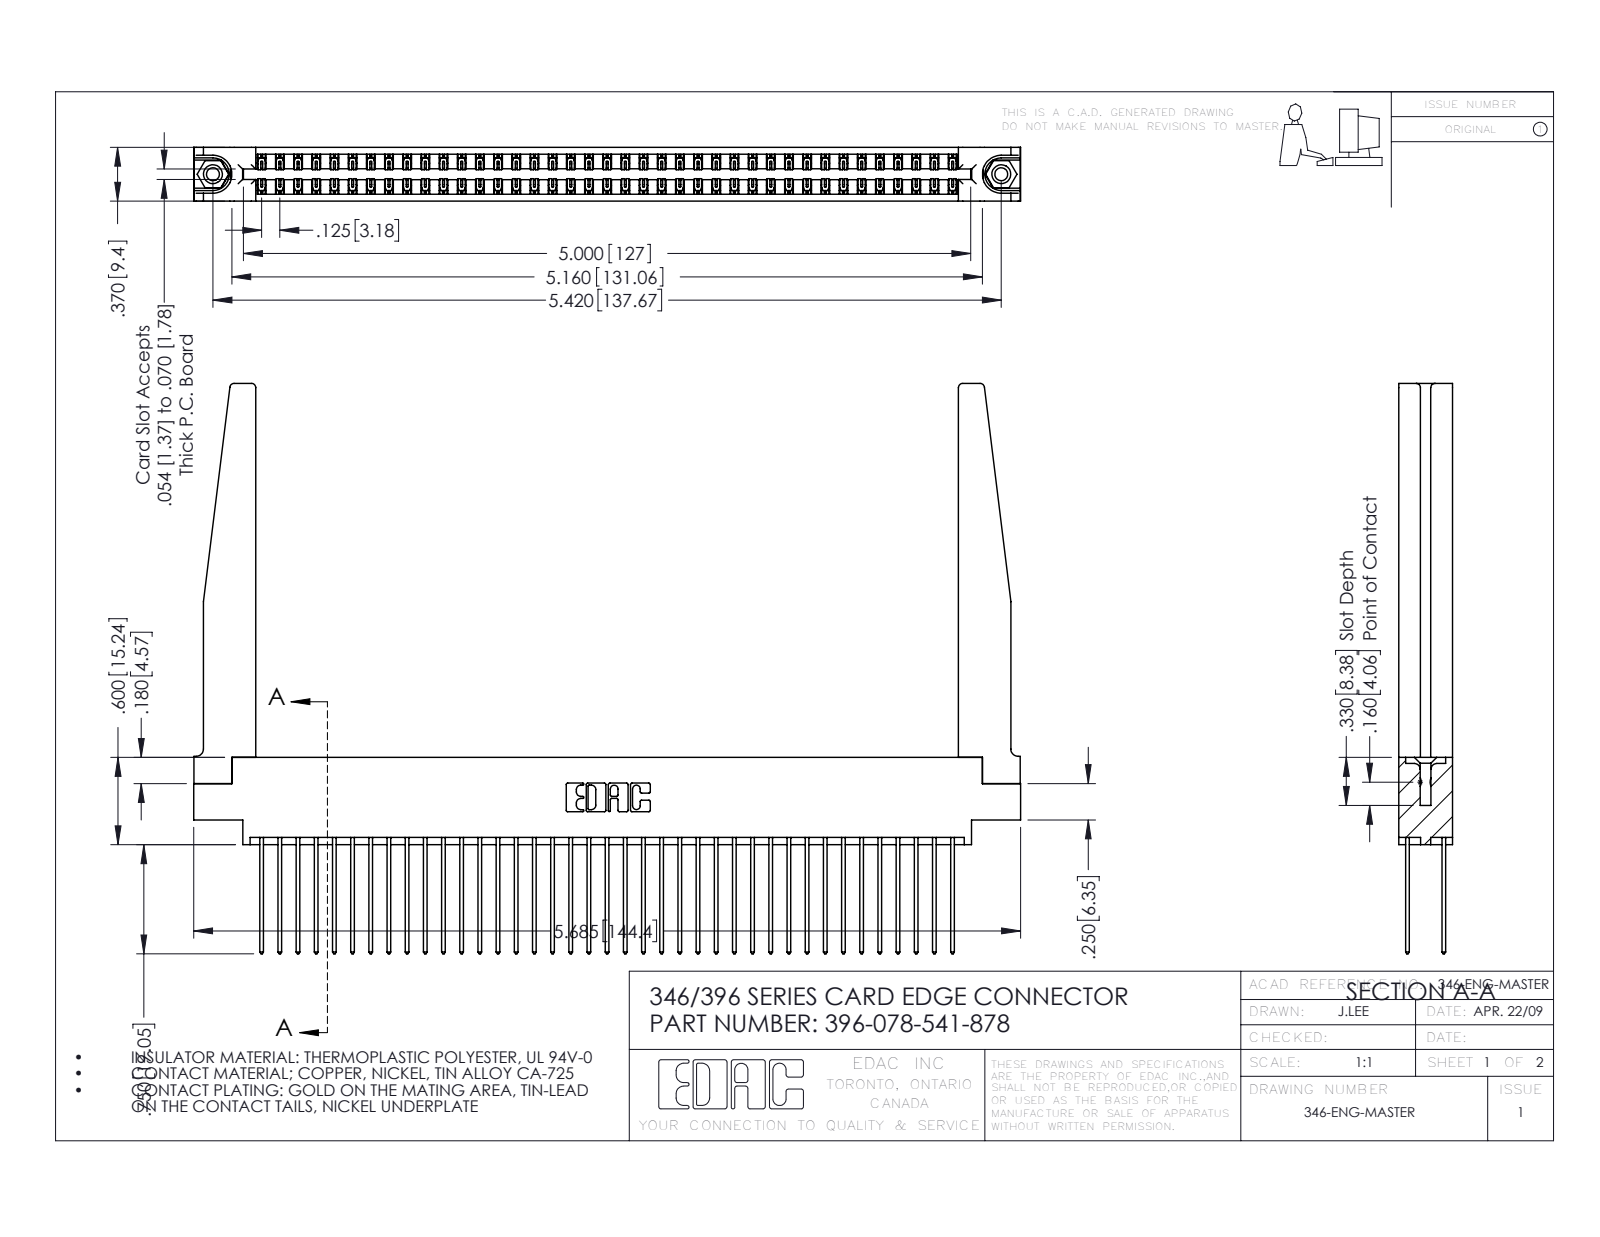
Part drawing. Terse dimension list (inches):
name: 346 Part_0.170 Offset - 0.156 Dia-TH; 346-220-078_345-220-078; 345-250-001_345-250-001-102; 396-078-541-878 (+1 more)
written by: SolidWorks 2016 (CONFIG_CONTROL_DESIGN)
unit: in
bodies: 83 solids, 4416 faces (2952 planar, 1412 cylindrical, 52 other)
size: 5.685 × 3.92 × 0.37
volume: 1.297 in³; area: 44.24 in²
holes: 2× ⌀0.089, 2× ⌀0.125, 2× ⌀0.156, 1× ⌀0.064
bosses: 2× ⌀0.155
rounds: 117× R0.006, 78× R0.01, 22× R0.01, 8× R0.03, 6× R0.007, 6× R0.031, 3× R0.026, 2× R0.014
face distances: 0.048, 0.322, 0.37, 0.072, 0.25, 0.298, 0.025, 0.275, 0.148, 0.15
hole spacings: 0.246, 5.211, 5.42
